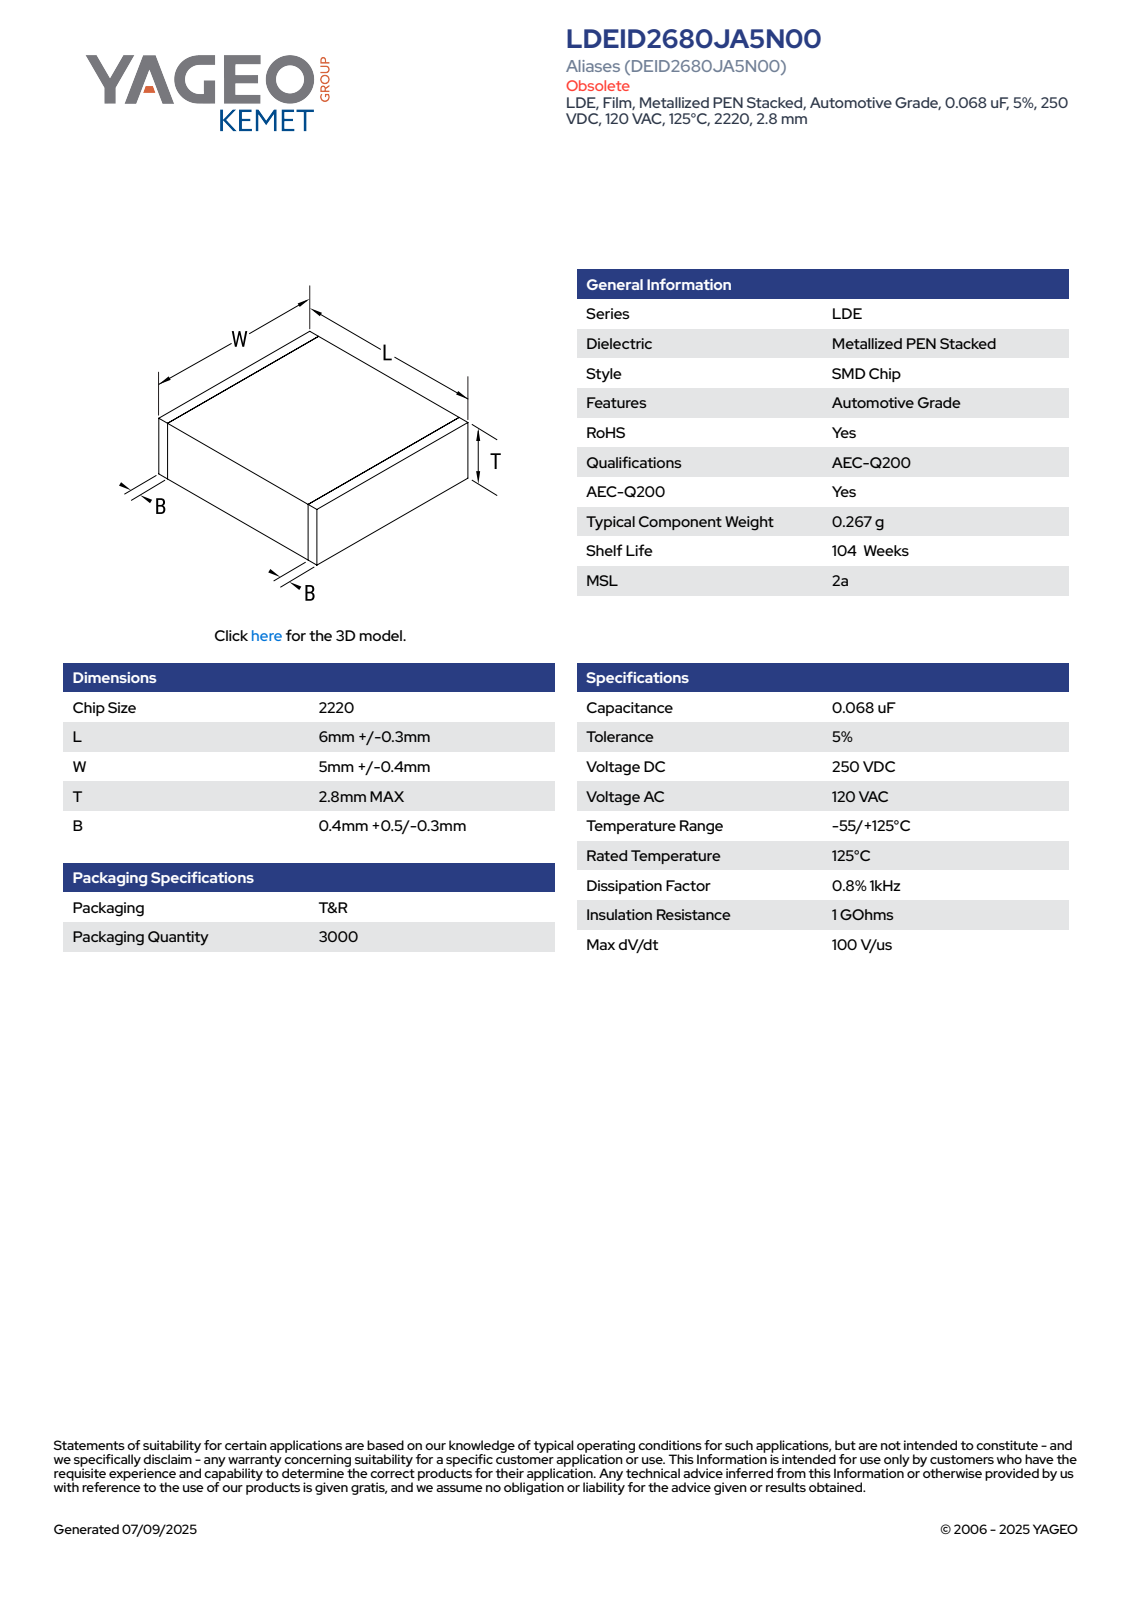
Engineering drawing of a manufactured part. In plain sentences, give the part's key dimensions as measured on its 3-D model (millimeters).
The part is named "CFS_LDELDB_2220_L6.3W5.4T2.8B0.9". Its 3-D file was written by "SolidWorks 2020 (AUTOMOTIVE_DESIGN)". It is 4 solids with 73 faces: 73 planar, 0 cylindrical and 0 other. Overall it measures 6.3 by 5.4 by 2.8 millimeters. Its volume is 94 cubic millimeters and its surface area 135 square millimeters. The main face-to-face distances are 2.78, 6.3, 5.38, 2.79, 5.39, 2.8, 5.4, 0.5, 5.8, 5.3.
